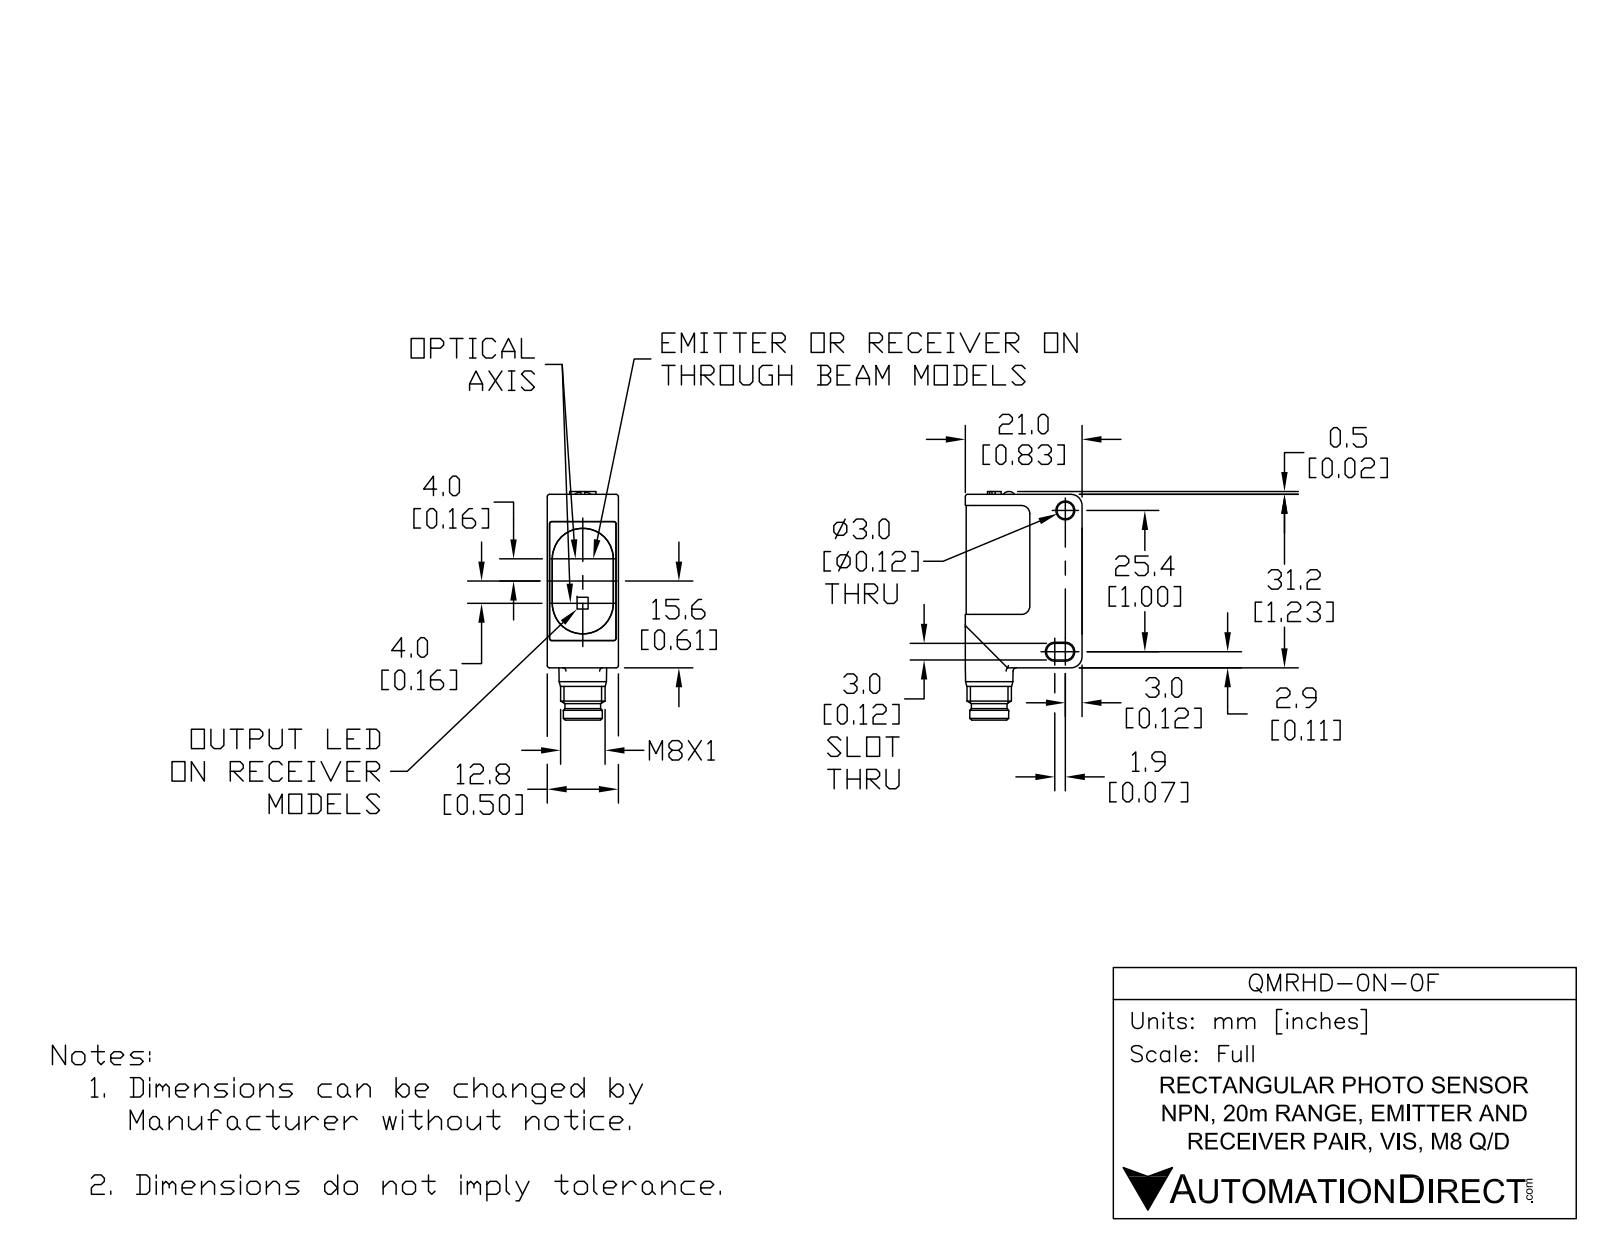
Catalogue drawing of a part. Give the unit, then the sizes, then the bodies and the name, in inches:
Units: inches
Overall size (bounding box): 1.619 × 0.827 × 0.504
Round holes (diameter × count): ⌀0.118 ×3, ⌀0.228 ×1
Round bosses / shafts (diameter × count): ⌀0.039 ×4, ⌀0.138 ×2, ⌀0.315 ×1, ⌀0.276 ×1, ⌀0.252 ×1
Partial cylindrical surfaces — rounded edges, fillets, slot ends (radius × count): R0.016 ×10, R0.02 ×9, R0.059 ×6, R0.024 ×4, R0.039 ×4, R0.006 ×2, R0.044 ×2, R0.065 ×2
Main face-to-face distances: 0.498, 0.02, 0.504, 0.11, 0.016, 0.492, 0.488, 0.482, 0.059, 0.711
Hole centre spacings: 0.04, 0.205, 0.245
Volume: 0.474 in³ · Surface area: 7.749 in²
Bodies: 7 solids, 272 faces (125 planar, 100 cylindrical, 47 other)
Part name (STEP PRODUCT): QMRHD-0N-0F
STEP written by: SolidWorks 2017 (AUTOMOTIVE_DESIGN)
